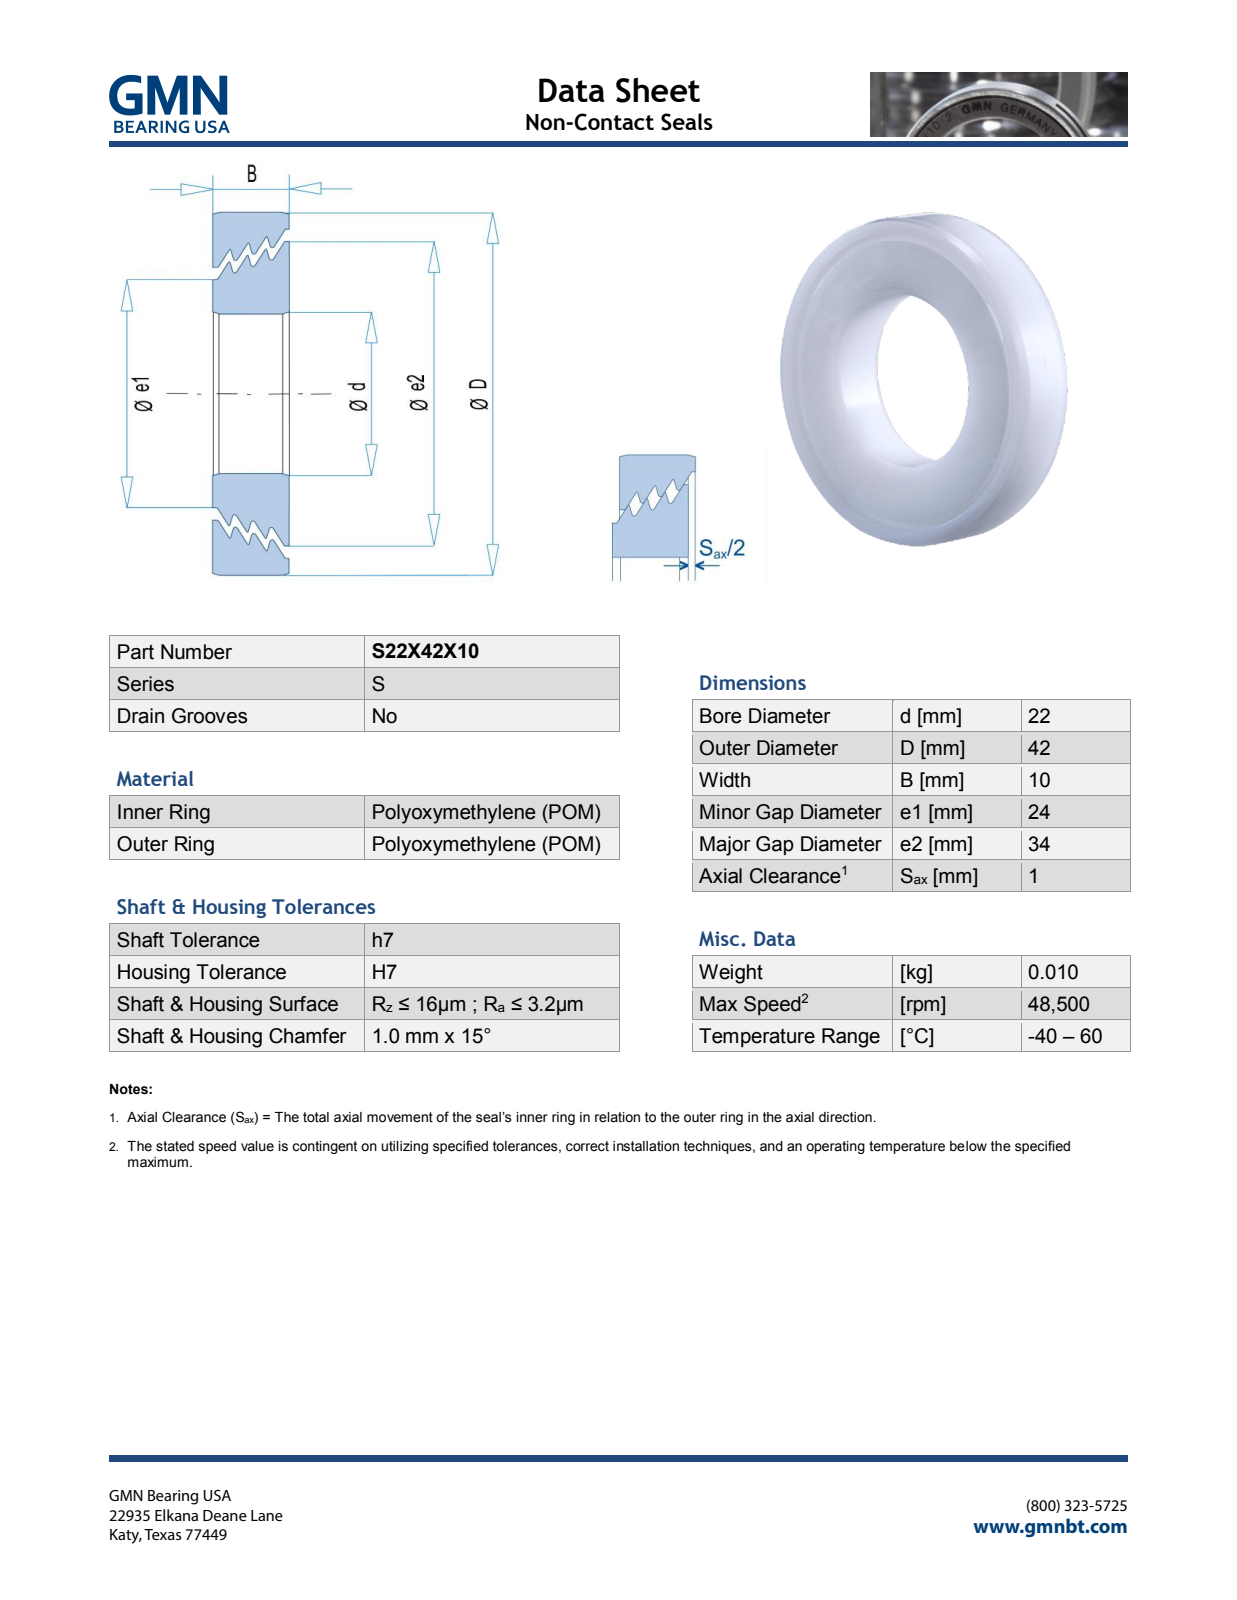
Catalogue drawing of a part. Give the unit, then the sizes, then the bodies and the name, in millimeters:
Units: millimetres
Overall size (bounding box): 42 × 42 × 10.07
Round holes (diameter × count): ⌀22 ×1, ⌀25.63 ×1, ⌀35.63 ×1
Round bosses / shafts (diameter × count): ⌀42 ×1, ⌀34 ×1, ⌀24 ×1
Main face-to-face distances: 10, 10.07, 1.53, 1.34, 1.15, 1.08, 1.14, 0.65, 0.88, 0.49
Volume: 9 236 mm³ · Surface area: 7 649 mm²
Bodies: 2 solids, 596 faces (516 planar, 12 cylindrical, 68 other)
Part name (STEP PRODUCT): S22X42X10_PRT
STEP written by: PRO/ENGINEER BY PARAMETRIC TECHNOLOGY CORPORATION, 2013150 (AUTOMOTIVE_DESIGN)
